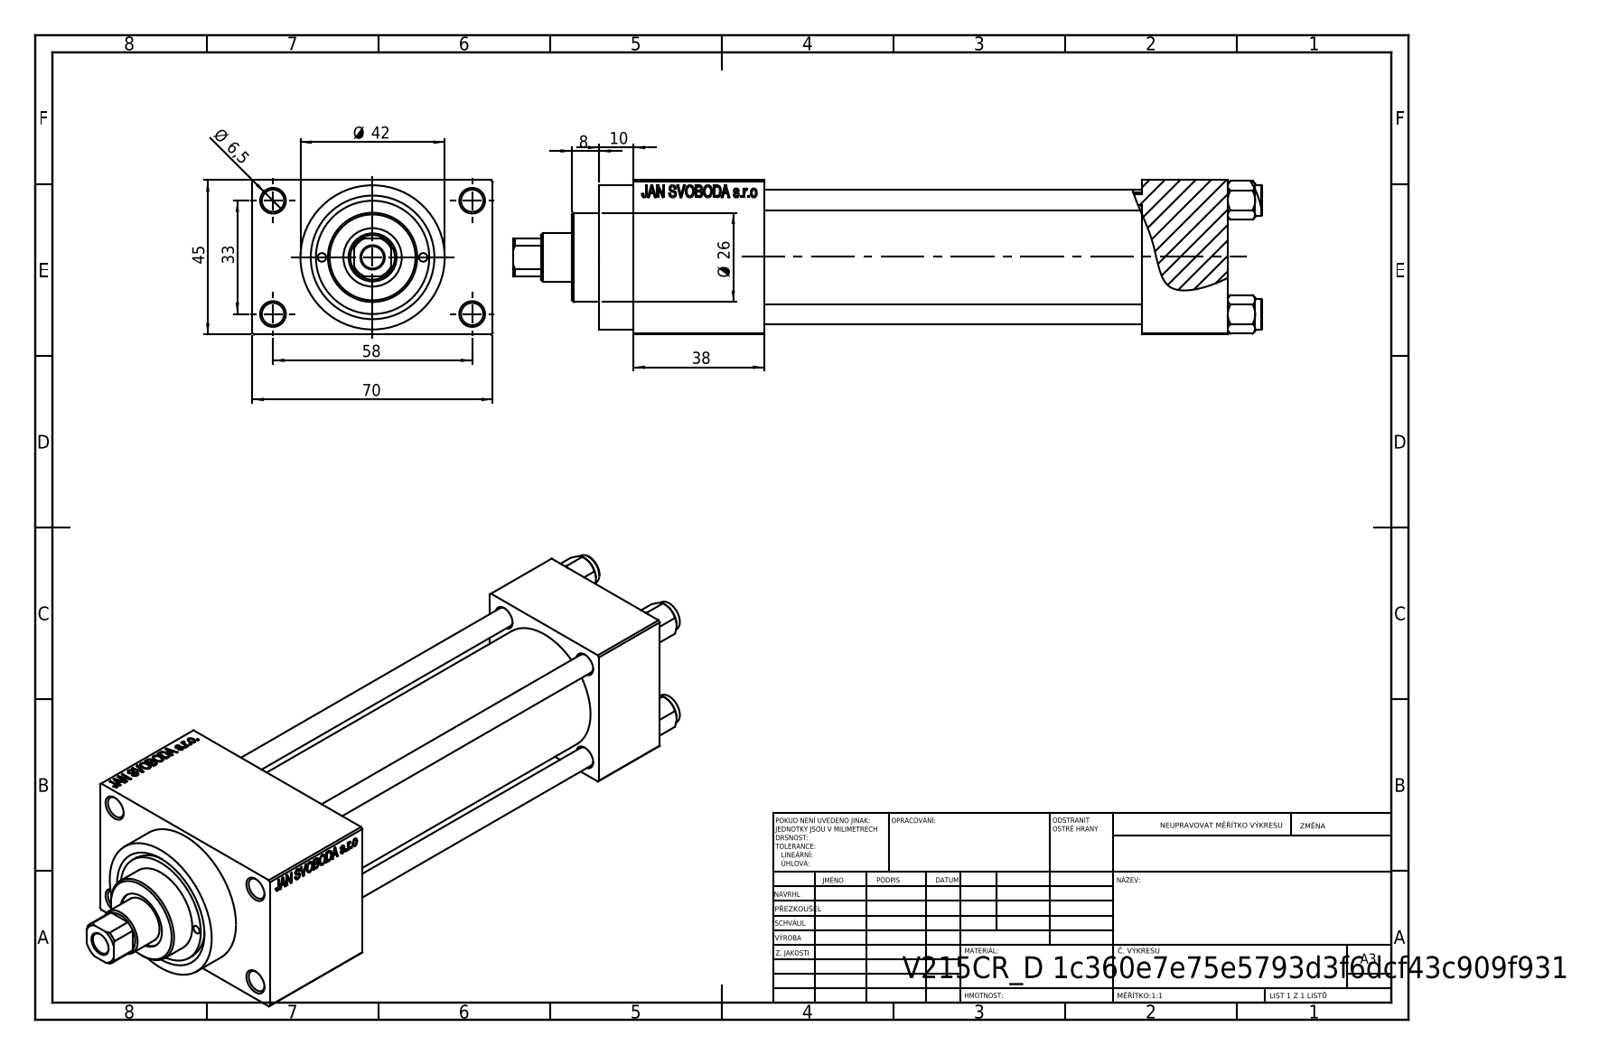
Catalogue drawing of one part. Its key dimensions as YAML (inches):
part_name: "V215_VC_A; V215CR_VCP_D; NUT_M5_D; V215CR_D_TYCINKA (+1 more)"
step_written_by: "SolidWorks 2019 (CONFIG_CONTROL_DESIGN)"
units: inches
bodies: {solids: 11, faces: 1110, planar: 498, cylindrical: 92, other: 520}
overall_size: [8.583, 2.756, 1.772]
volume: 16.23
surface_area: 148.4
round_holes:
  - {diameter: 0.256, count: 5}
  - {diameter: 0.236, count: 4}
  - {diameter: 0.098, count: 2}
  - {diameter: 0.276, count: 2}
  - {diameter: 0.518, count: 2}
  - {diameter: 0.787, count: 2}
  - {diameter: 0.551, count: 1}
  - {diameter: 0.669, count: 1}
  - {diameter: 0.945, count: 1}
  - {diameter: 1.26, count: 1}
  - {diameter: 1.299, count: 1}
round_bosses_or_shafts:
  - {diameter: 0.354, count: 4}
  - {diameter: 1.654, count: 1}
  - {diameter: 1.496, count: 1}
  - {diameter: 1.024, count: 1}
partial_cylinders:
  - {radius: 0.256, count: 1}
face_to_face_distances: [1.772, 0.984, 0.492, 4.331, 5.315, 2.264, 5.827, 1.496, 6.811, 2.756]
hole_center_spacings: [0.488, 0.657, 0.858, 0.924, 1.307, 1.314, 1.392, 1.396]
